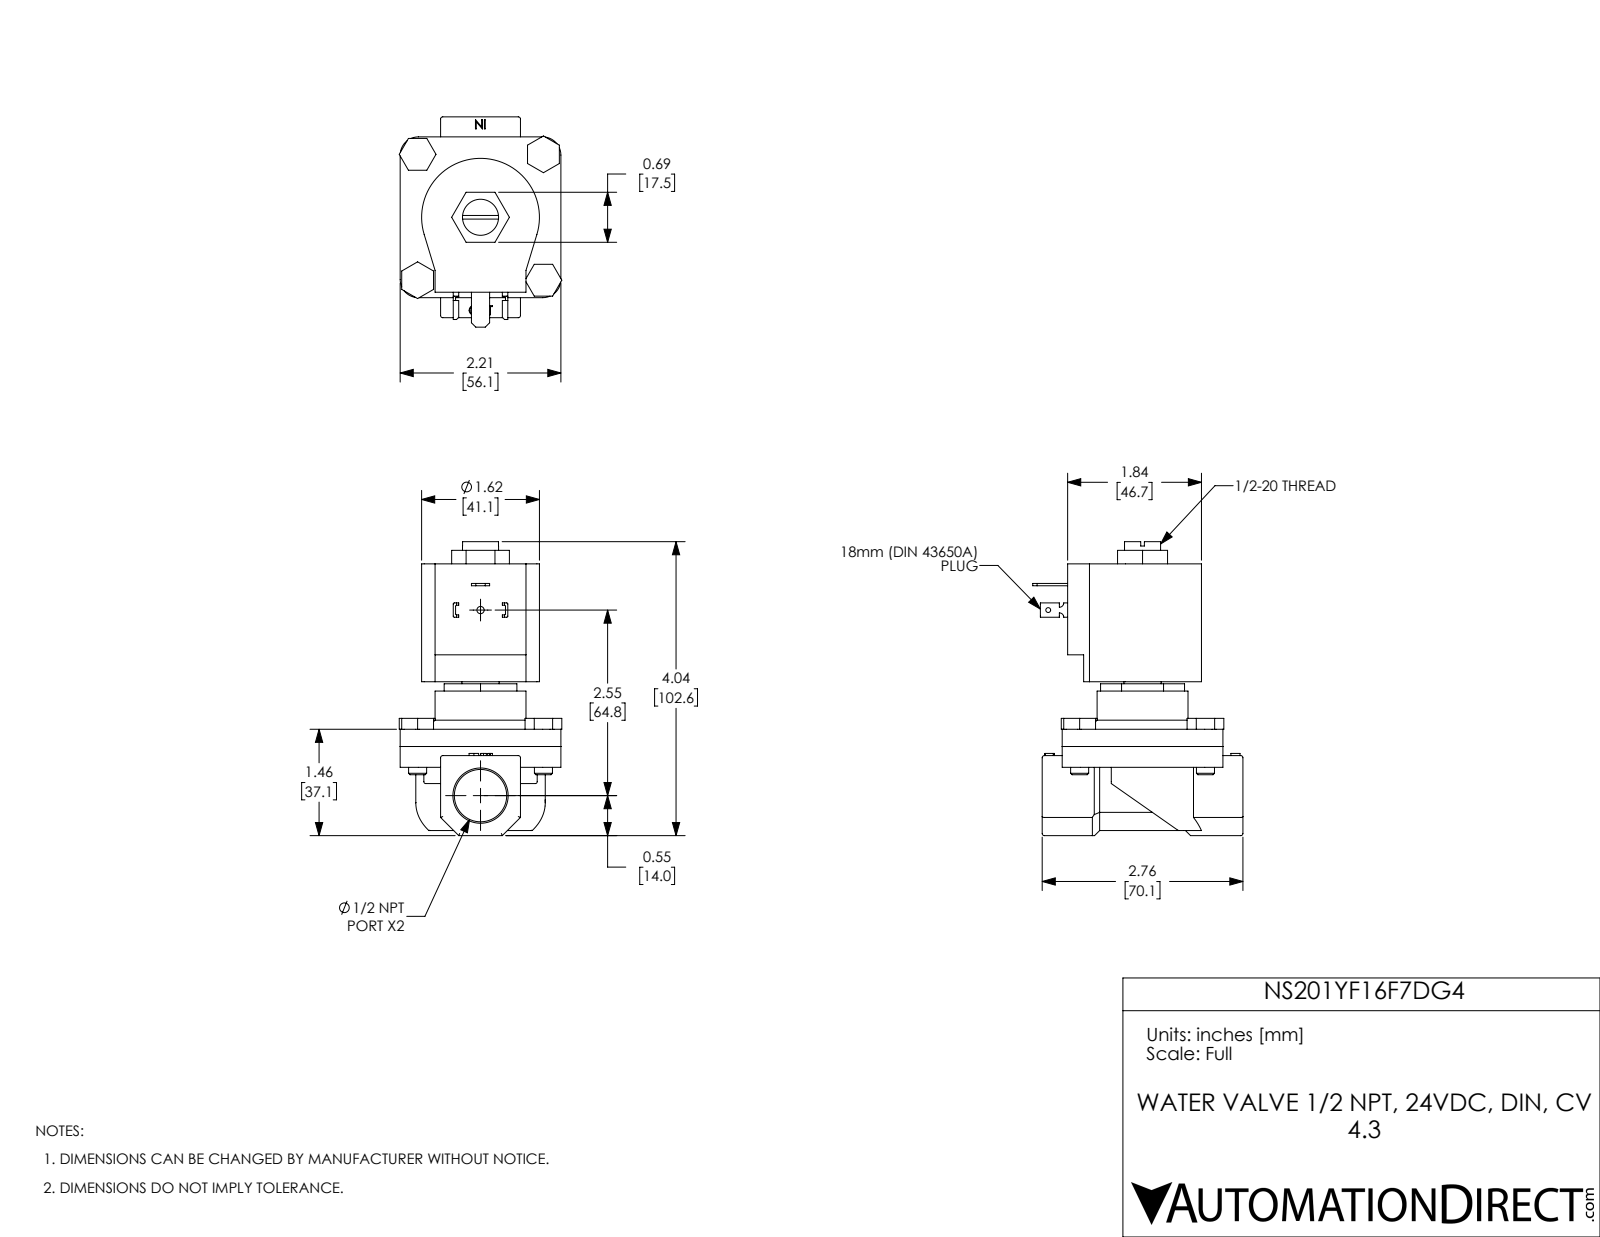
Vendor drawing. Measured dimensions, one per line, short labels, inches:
name: NS201YF16F7DG4
written by: SolidWorks 2017 (AUTOMOTIVE_DESIGN)
unit: in
bodies: 11 solids, 330 faces (196 planar, 99 cylindrical, 35 other)
size: 4.04 × 2.89 × 2.235
volume: 9.842 in³; area: 63.61 in²
holes: 4× ⌀0.25, 1× ⌀0.067, 1× ⌀0.1, 1× ⌀0.496, 1× ⌀0.512, 1× ⌀0.72, 1× ⌀1.155
bosses: 4× ⌀0.248, 1× ⌀1.25
rounds: 15× R0.03, 8× R0.015, 4× R0.25, 2× R0.06, 1× R0.81, 1× R0.89
face distances: 0.237, 0.237, 2.51, 2.51, 2.273, 0.556, 1.654, 0.286, 0.286, 0.523
hole spacings: 1.223, 1.73, 2.446, 2.55
